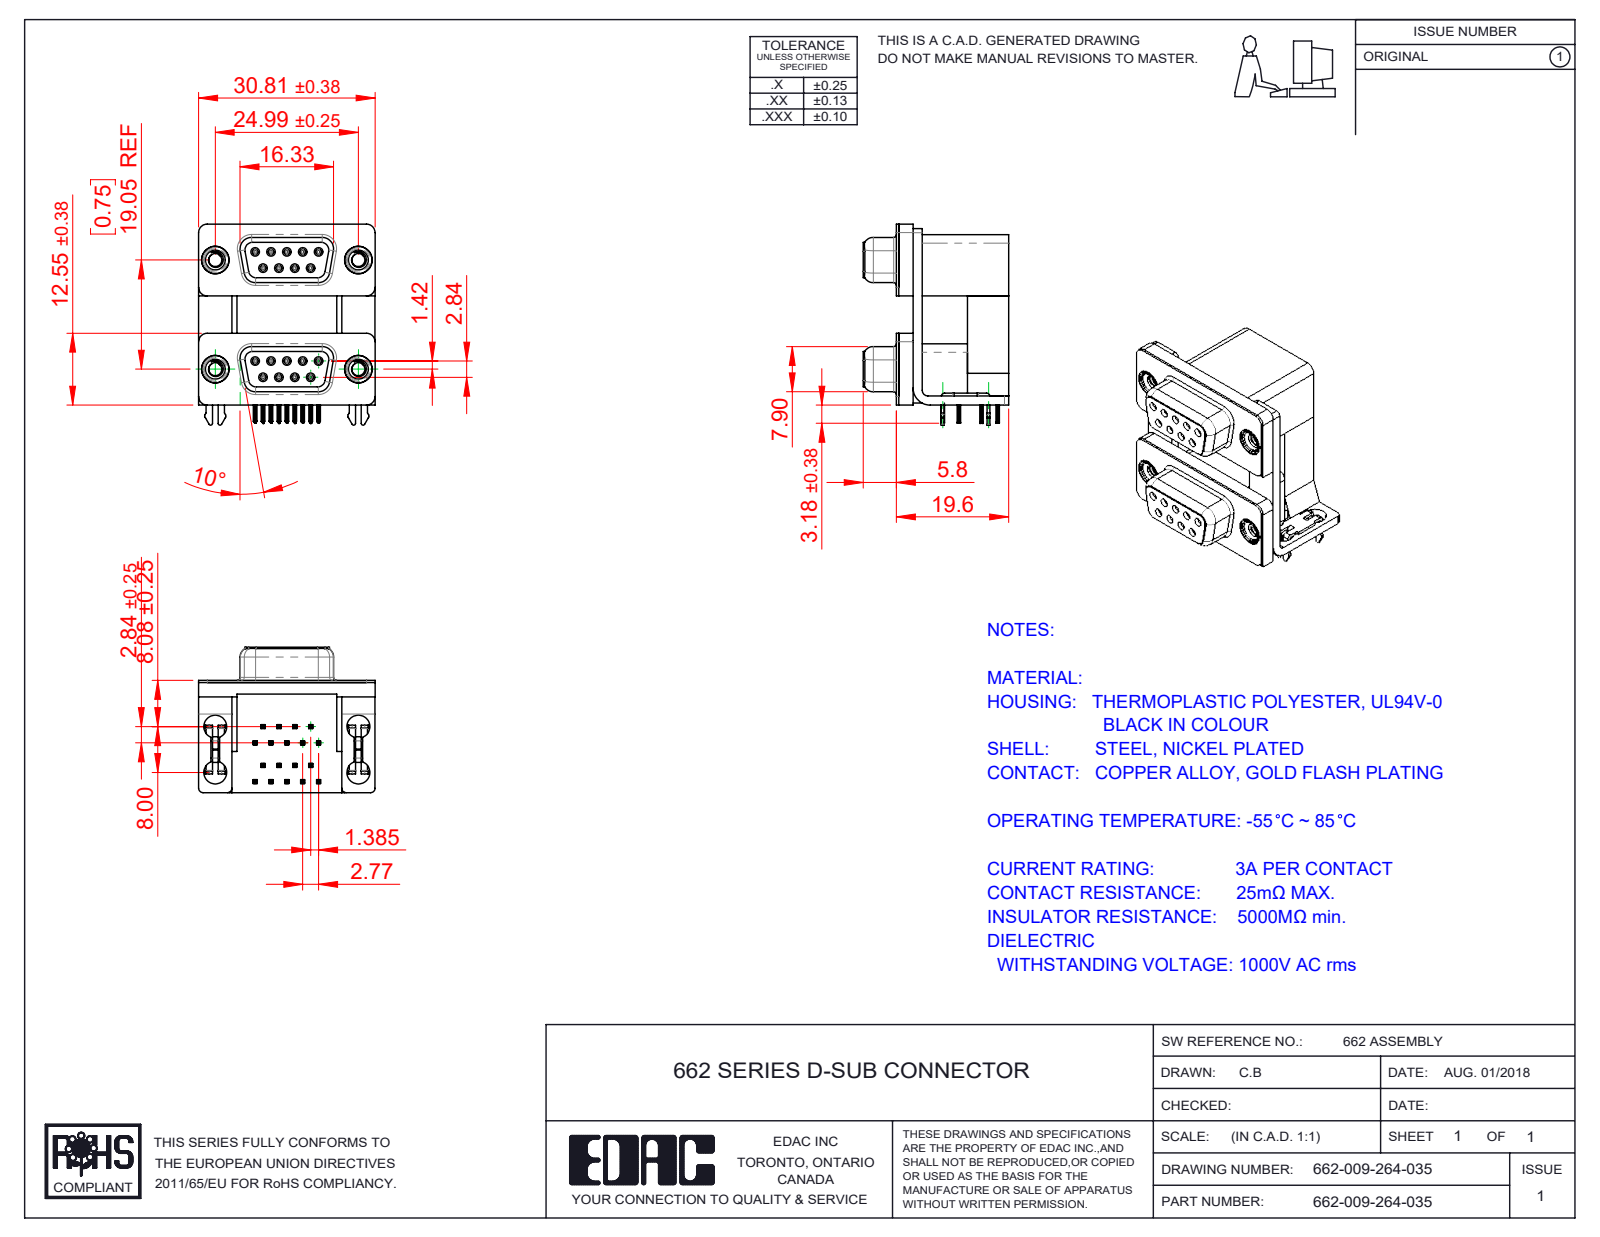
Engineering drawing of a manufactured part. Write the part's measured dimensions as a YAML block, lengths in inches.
part_name: "662 Contact Top Upper_M; 662 Contact Bottom Lower; 662 Housing Lower_09 Contacts; 662 Contact Bottom Upper_M (+8 more)"
step_written_by: "SolidWorks 2020 (CONFIG_CONTROL_DESIGN)"
units: inches
bodies: {solids: 31, faces: 3262, planar: 1476, cylindrical: 846, other: 940}
overall_size: [1.382, 1.213, 1]
volume: 0.69
surface_area: 20.87
round_holes:
  - {diameter: 0.031, count: 18}
  - {diameter: 0.035, count: 18}
  - {diameter: 0.157, count: 8}
  - {diameter: 0.089, count: 4}
  - {diameter: 0.138, count: 4}
  - {diameter: 0.189, count: 4}
  - {diameter: 0.197, count: 4}
round_bosses_or_shafts:
  - {diameter: 0.047, count: 18}
  - {diameter: 0.193, count: 4}
  - {diameter: 0.187, count: 4}
  - {diameter: 0.154, count: 4}
partial_cylinders:
  - {radius: 0.004, count: 146}
  - {radius: 0.006, count: 72}
  - {radius: 0.014, count: 36}
  - {radius: 0.013, count: 18}
  - {radius: 0.053, count: 16}
  - {radius: 0.02, count: 12}
  - {radius: 0.059, count: 12}
  - {radius: 0.01, count: 10}
face_to_face_distances: [0.098, 0.016, 0.657, 0.756, 0.75, 0.114, 0.472, 0.488, 0.283, 0.374]
hole_center_spacings: [0.124, 0.109, 0.758, 0.75, 0.218, 0.781, 0.641, 0.863]
